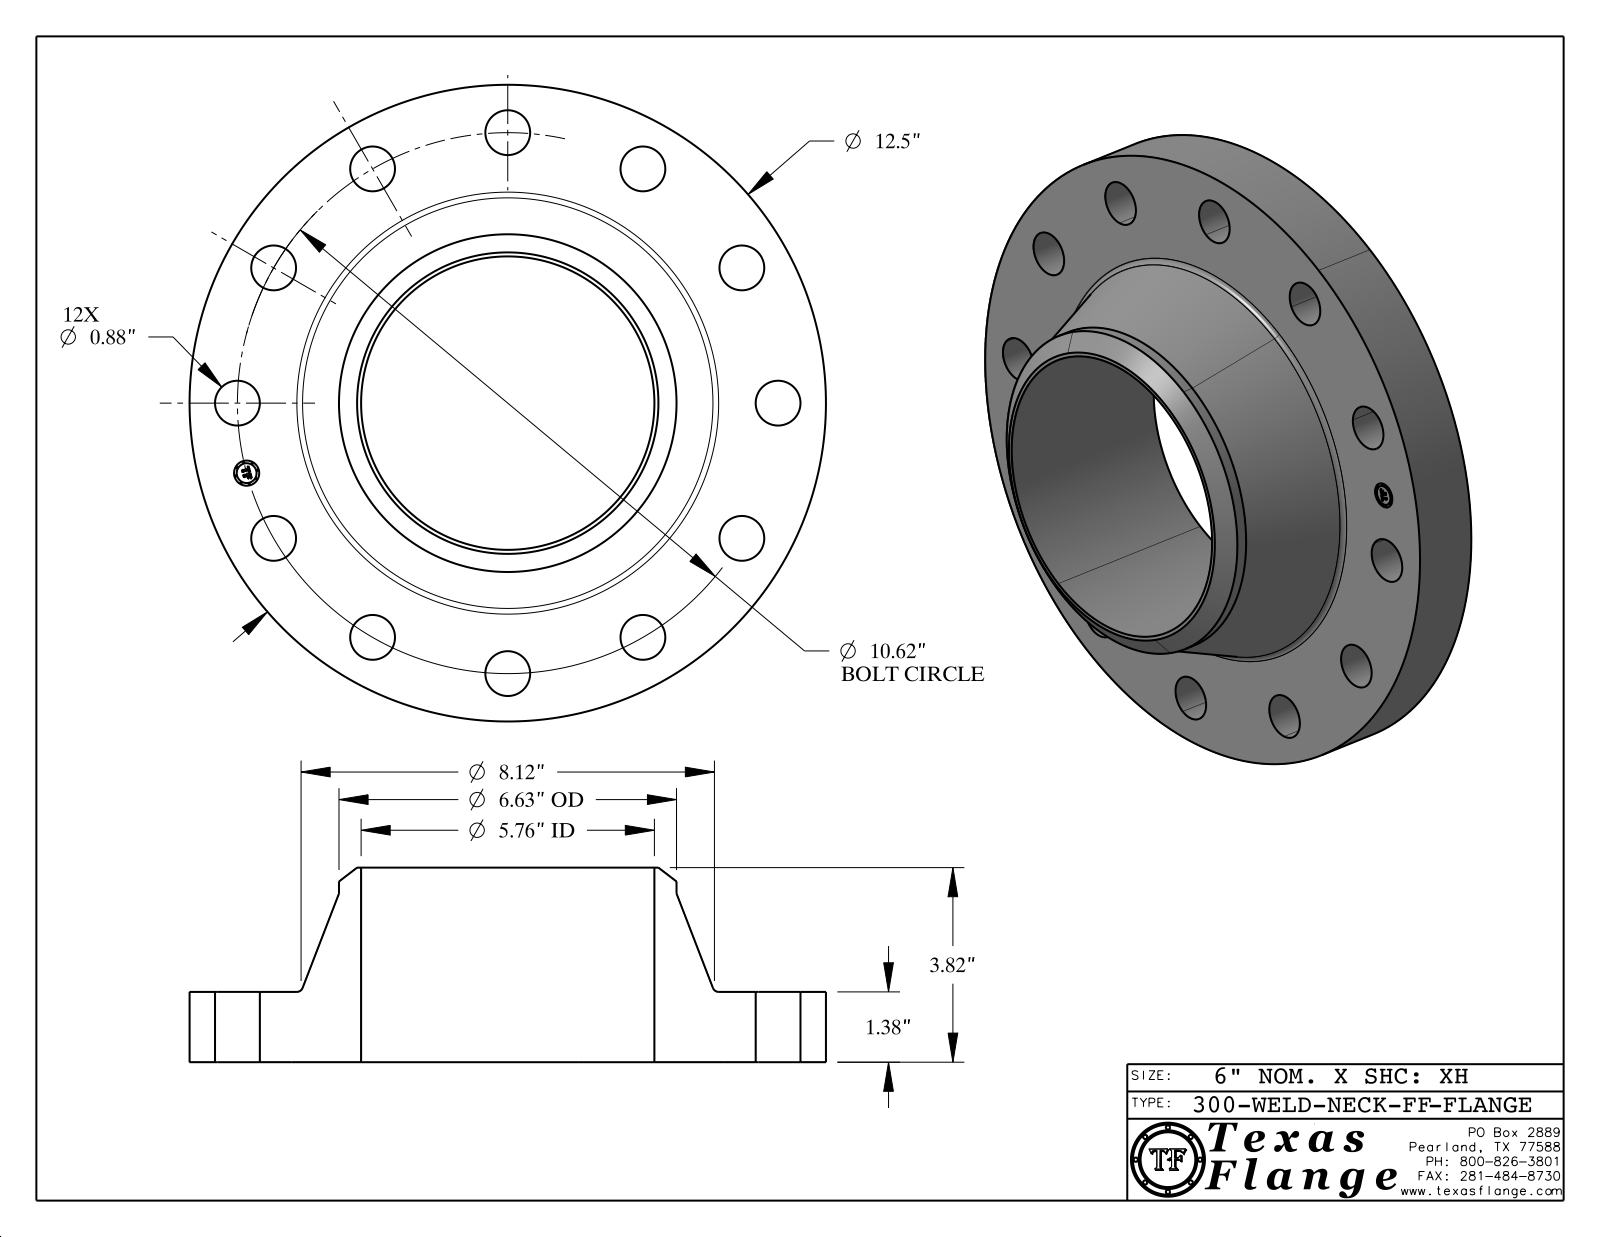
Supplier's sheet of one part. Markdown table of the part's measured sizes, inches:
| quantity | value |
| --- | --- |
| part name | 300-WELD-NECK-FF |
| STEP written by | CATIA V5 STEP AP214 (AUTOMOTIVE_DESIGN) |
| units | inches |
| bodies | 1 solid, 425 faces (369 planar, 50 cylindrical, 6 other) |
| overall size | 12.5 × 12.5 × 3.82 |
| volume | 159.1 in³ |
| surface area | 384.8 in² |
| round holes (diameter × count) | 0.88 × 12, 0.495 × 1, 5.761 × 1 |
| round bosses / shafts (diameter × count) | 0.03 × 8, 12.5 × 1, 6.63 × 1, 0.39 × 1 |
| main face-to-face distances | 1.38, 3.82, 2.44, 1.365, 0.015, 2.455, 0.148, 0.145, 0.027, 0.096 |
| hole center spacings | 5.31, 10.258, 2.749, 7.509, 9.197, 10.62, 5.31, 2.748 |
